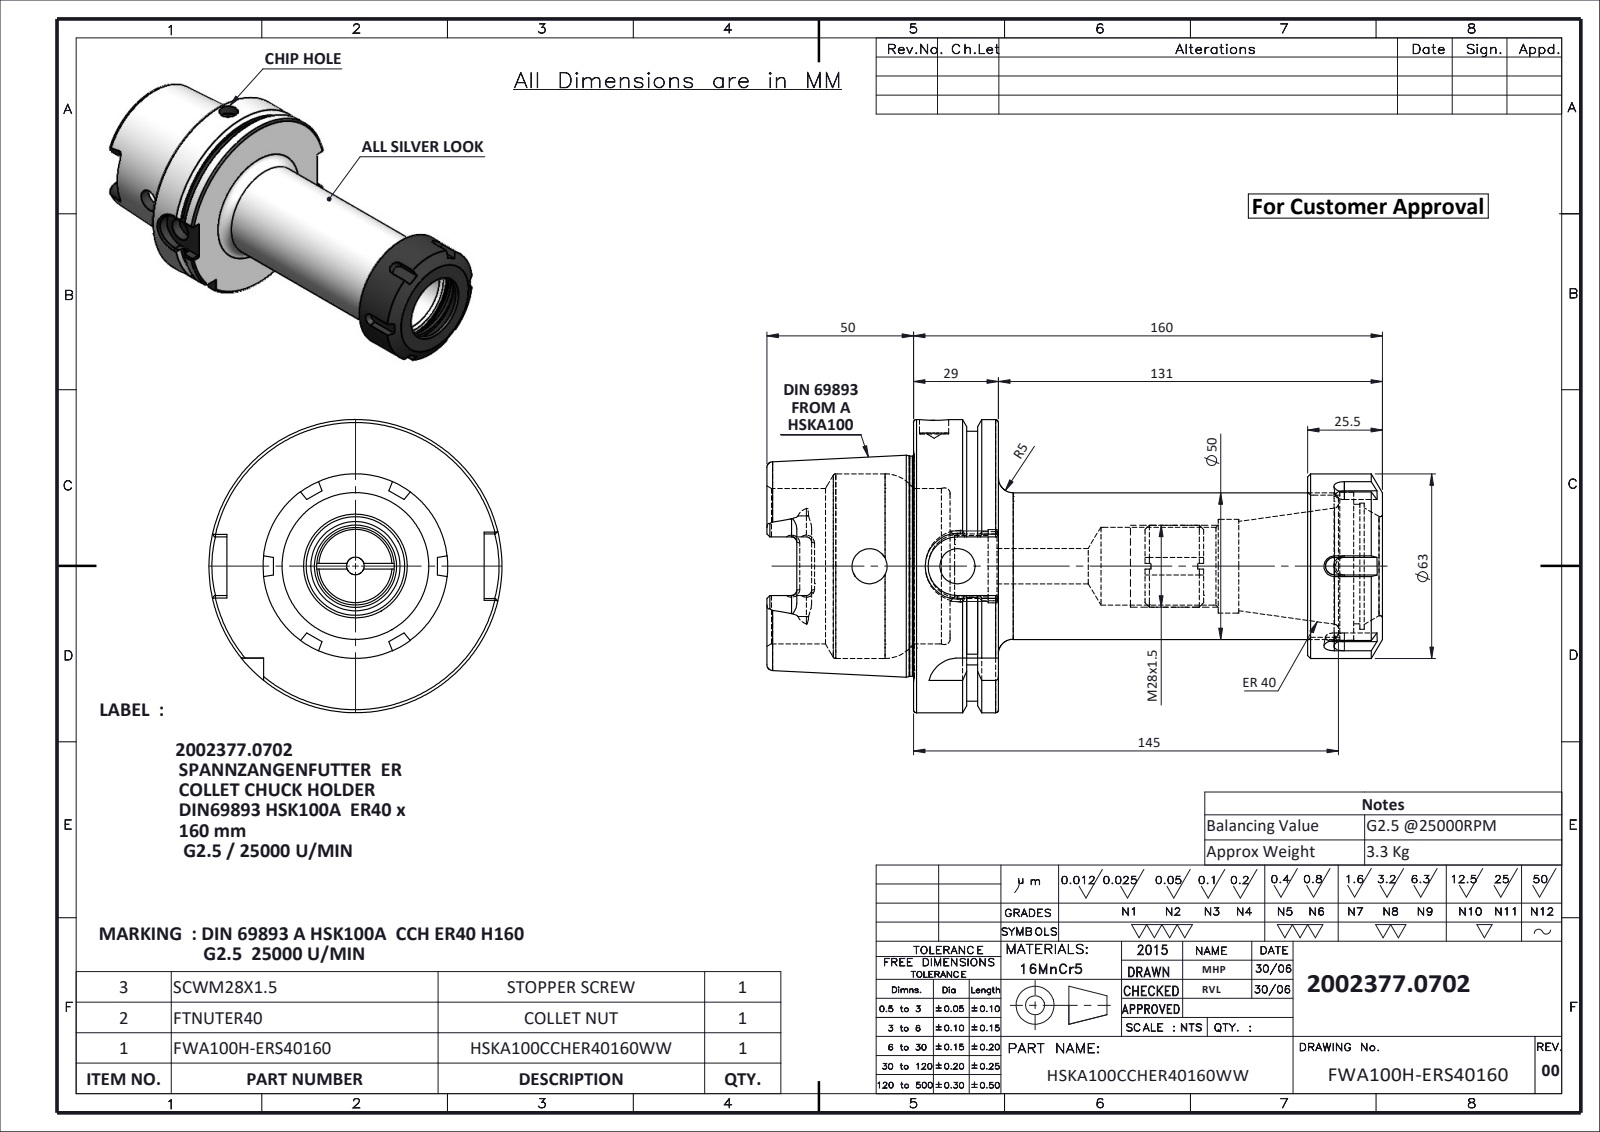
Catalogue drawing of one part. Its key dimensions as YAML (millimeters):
part_name: "FTSCWM28X150; HSKA100CCHER40160WW; FWA100H-ERS40160; FTNUTER40"
step_written_by: "SolidWorks 2024 (CONFIG_CONTROL_DESIGN)"
units: millimeters
bodies: {solids: 3, faces: 257, planar: 95, cylindrical: 66, other: 96}
overall_size: [210, 100, 100]
volume: 462021
surface_area: 92493
round_holes:
  - {diameter: 12, count: 3}
  - {diameter: 6, count: 1}
  - {diameter: 10, count: 1}
  - {diameter: 21, count: 1}
  - {diameter: 25, count: 1}
  - {diameter: 26.5, count: 1}
  - {diameter: 32, count: 1}
  - {diameter: 40.75, count: 1}
  - {diameter: 43, count: 1}
  - {diameter: 48.5, count: 1}
  - {diameter: 50.5, count: 1}
  - {diameter: 53, count: 1}
round_bosses_or_shafts:
  - {diameter: 100, count: 1}
  - {diameter: 92, count: 1}
  - {diameter: 75.16, count: 1}
  - {diameter: 50, count: 1}
  - {diameter: 28, count: 1}
partial_cylinders:
  - {radius: 1.8, count: 6}
  - {radius: 4.88, count: 4}
  - {radius: 10, count: 2}
  - {radius: 11, count: 1}
face_to_face_distances: [29, 12.5, 16.5, 50, 79, 25.5, 134.5, 160, 147.5, 131]
hole_center_spacings: [1.5, 30]
